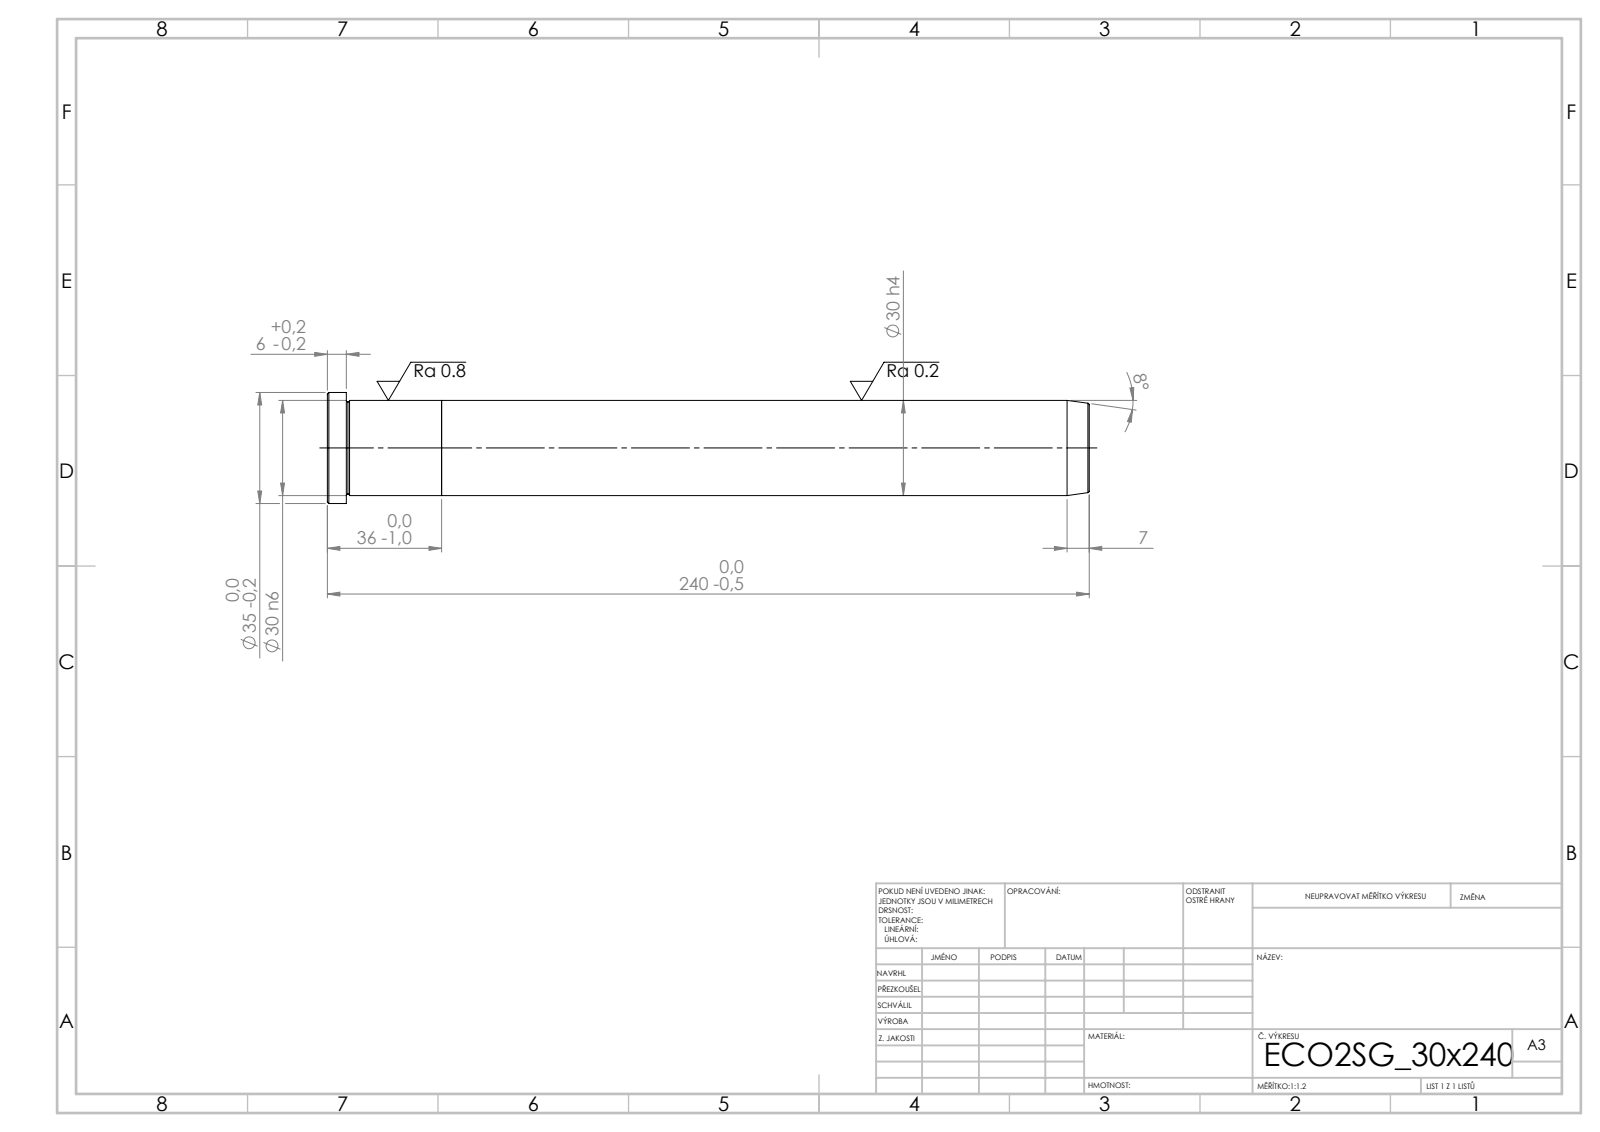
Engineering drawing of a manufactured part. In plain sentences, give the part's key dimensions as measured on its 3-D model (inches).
Its 3-D file was written by "SolidWorks 2019 (CONFIG_CONTROL_DESIGN)". It is 2 solids with 21 faces: 5 planar, 6 cylindrical and 10 other. Overall it measures 9.449 by 1.378 by 1.378 inches. Its volume is 10.42 cubic inches and its surface area 40.22 square inches. Round bosses or shafts: 1 of diameter 1.378, 1 of diameter 1.181. The main face-to-face distances are 1.417, 8.031, 9.449, 9.213, 1.181, 0.236.
